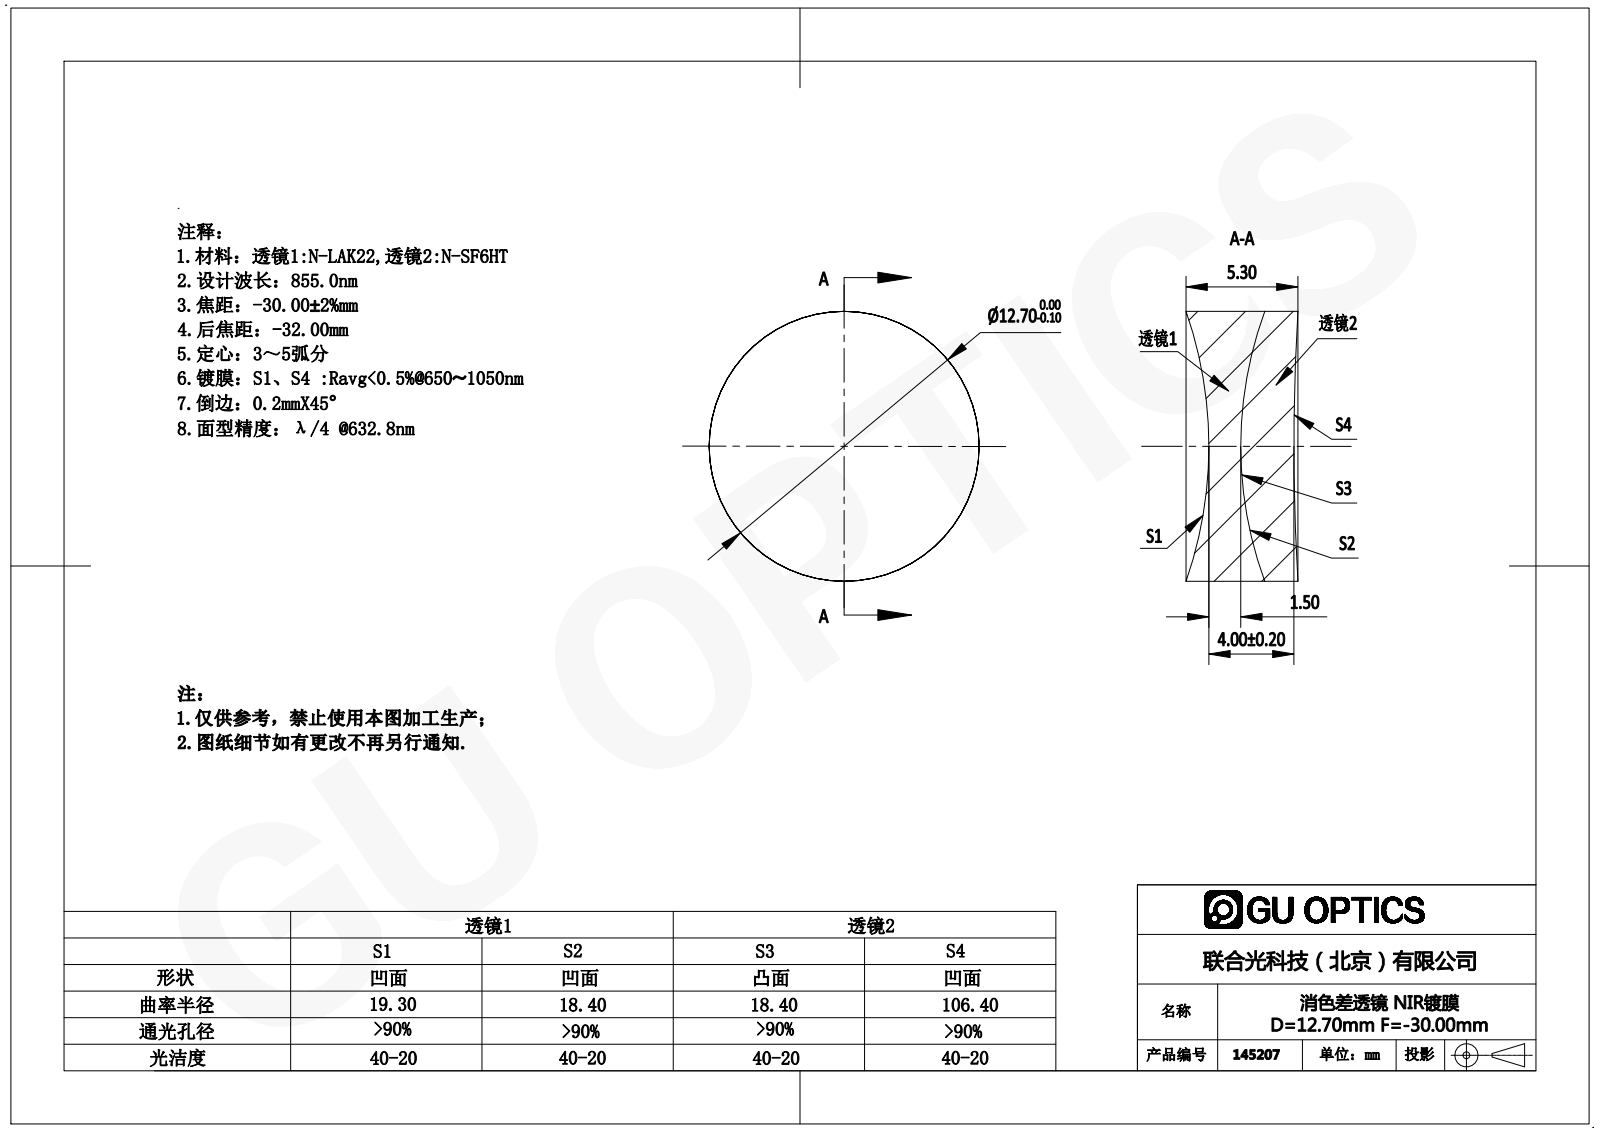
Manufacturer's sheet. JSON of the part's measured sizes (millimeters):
{"part_name": "145207", "step_written_by": "SolidWorks 2016 (AUTOMOTIVE_DESIGN)", "units": "millimeters", "bodies": {"solids": 2, "faces": 12, "planar": 0, "cylindrical": 4, "other": 8}, "overall_size": [12.7, 12.7, 5.26], "volume_mm3": 586, "surface_area_mm2": 729, "round_bosses_or_shafts": [[12.7, 1]]}
